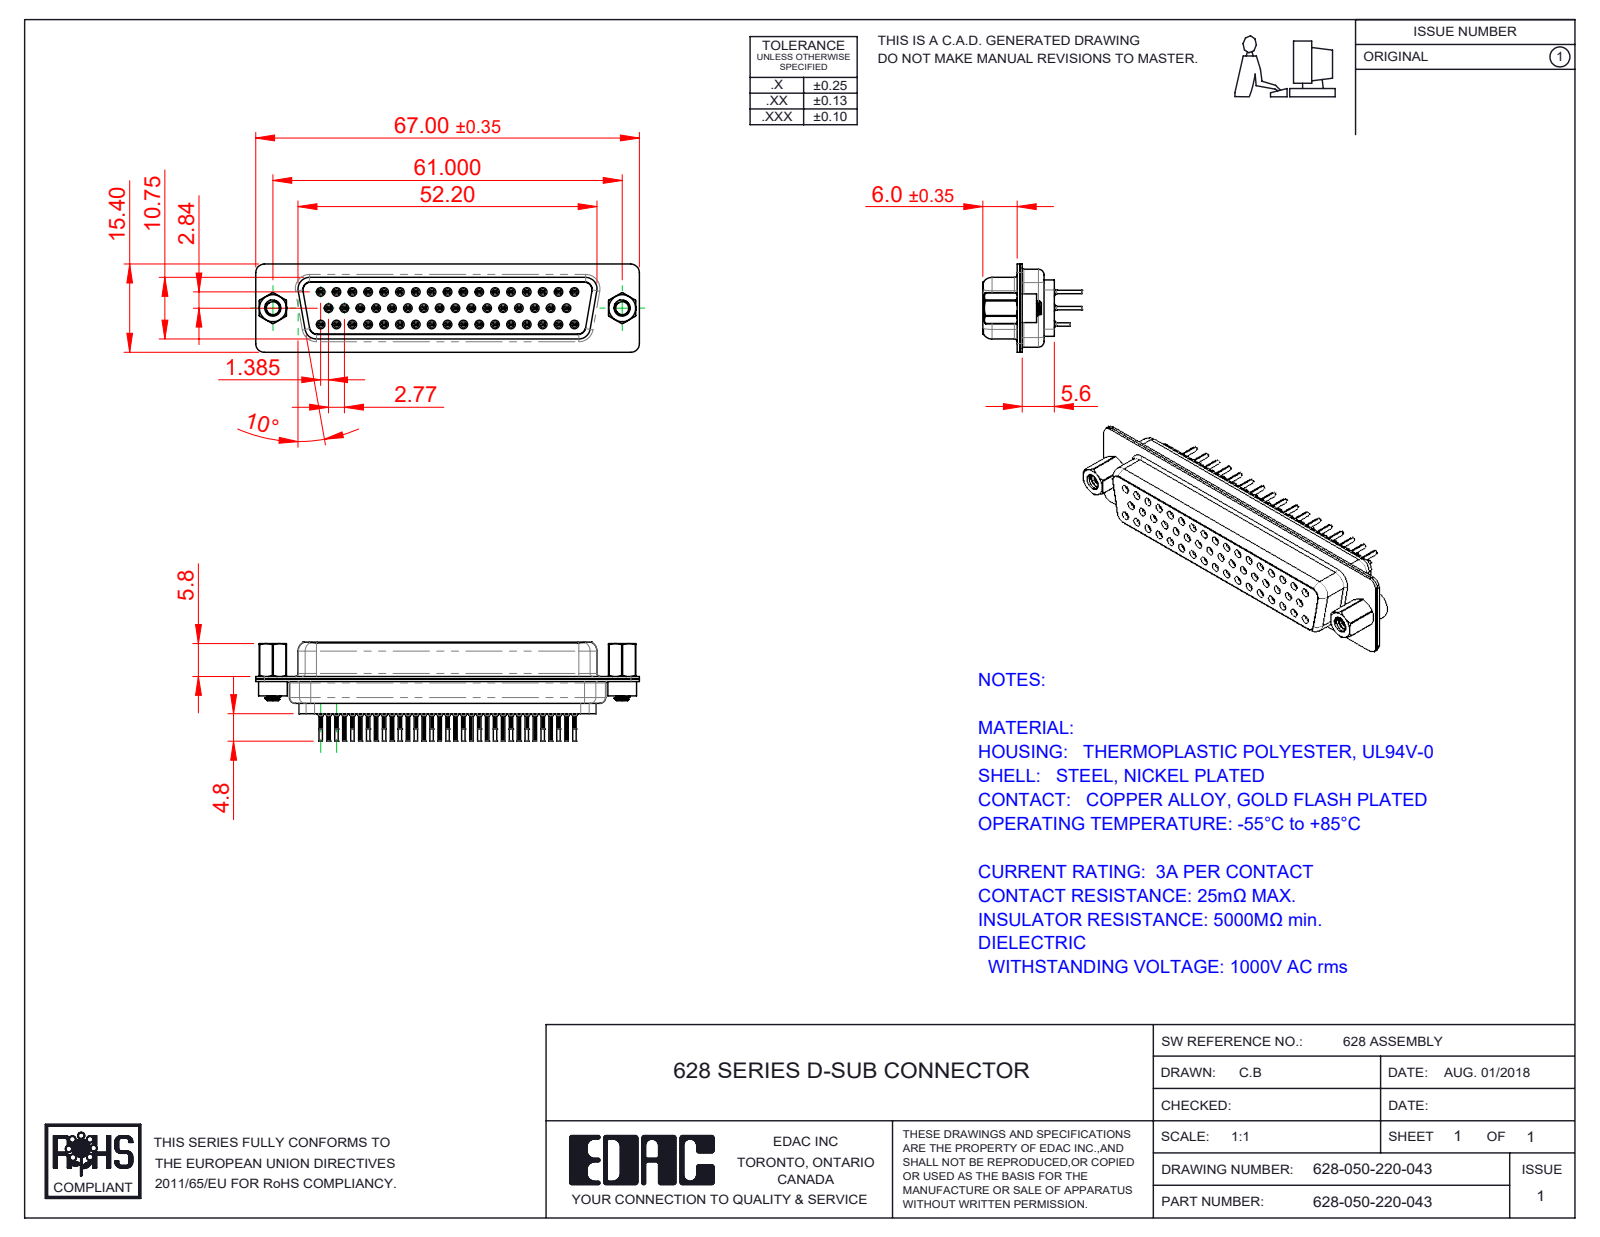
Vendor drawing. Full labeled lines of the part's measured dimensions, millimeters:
Part name (STEP PRODUCT): 628 Housing_50 LP; 628 Contact Row 1_20L; 628 4-40 Threaded Rivet; 628-050-220-043 (+5 more)
STEP written by: SolidWorks 2020 (CONFIG_CONTROL_DESIGN)
Units: millimetres
Bodies: 57 solids, 6751 faces (1639 planar, 1857 cylindrical, 3255 other)
Overall size (bounding box): 67 × 17.3 × 15.4
Volume: 6 929 mm³ · Surface area: 15 748 mm²
Round holes (diameter × count): ⌀0.2 ×50, ⌀0.8 ×50, ⌀0.9 ×50, ⌀1.1 ×50, ⌀1.6 ×50, ⌀1.7 ×17, ⌀2.26 ×2, ⌀2.29 ×2, ⌀4 ×2, ⌀4.05 ×2, ⌀4.85 ×2
Round bosses / shafts (diameter × count): ⌀2 ×50, ⌀1.5 ×50, ⌀1.2 ×50, ⌀0.6 ×50, ⌀5 ×2, ⌀4.95 ×2, ⌀4.8 ×2, ⌀2.79 ×2
Partial cylindrical surfaces — rounded edges, fillets, slot ends (radius × count): R0.1 ×100, R0.28 ×33, R1.5 ×16, R2 ×12, R1.35 ×8, R0.25 ×4, R0.5 ×4, R0.6 ×4
Main face-to-face distances: 0.45, 0.4, 11.33, 1.87, 10.3, 0.9, 6.05, 6.5, 1.8, 6
Hole centre spacings: 3.16, 2.77, 5.54, 8.31, 11.08, 13.85, 16.62, 19.39
